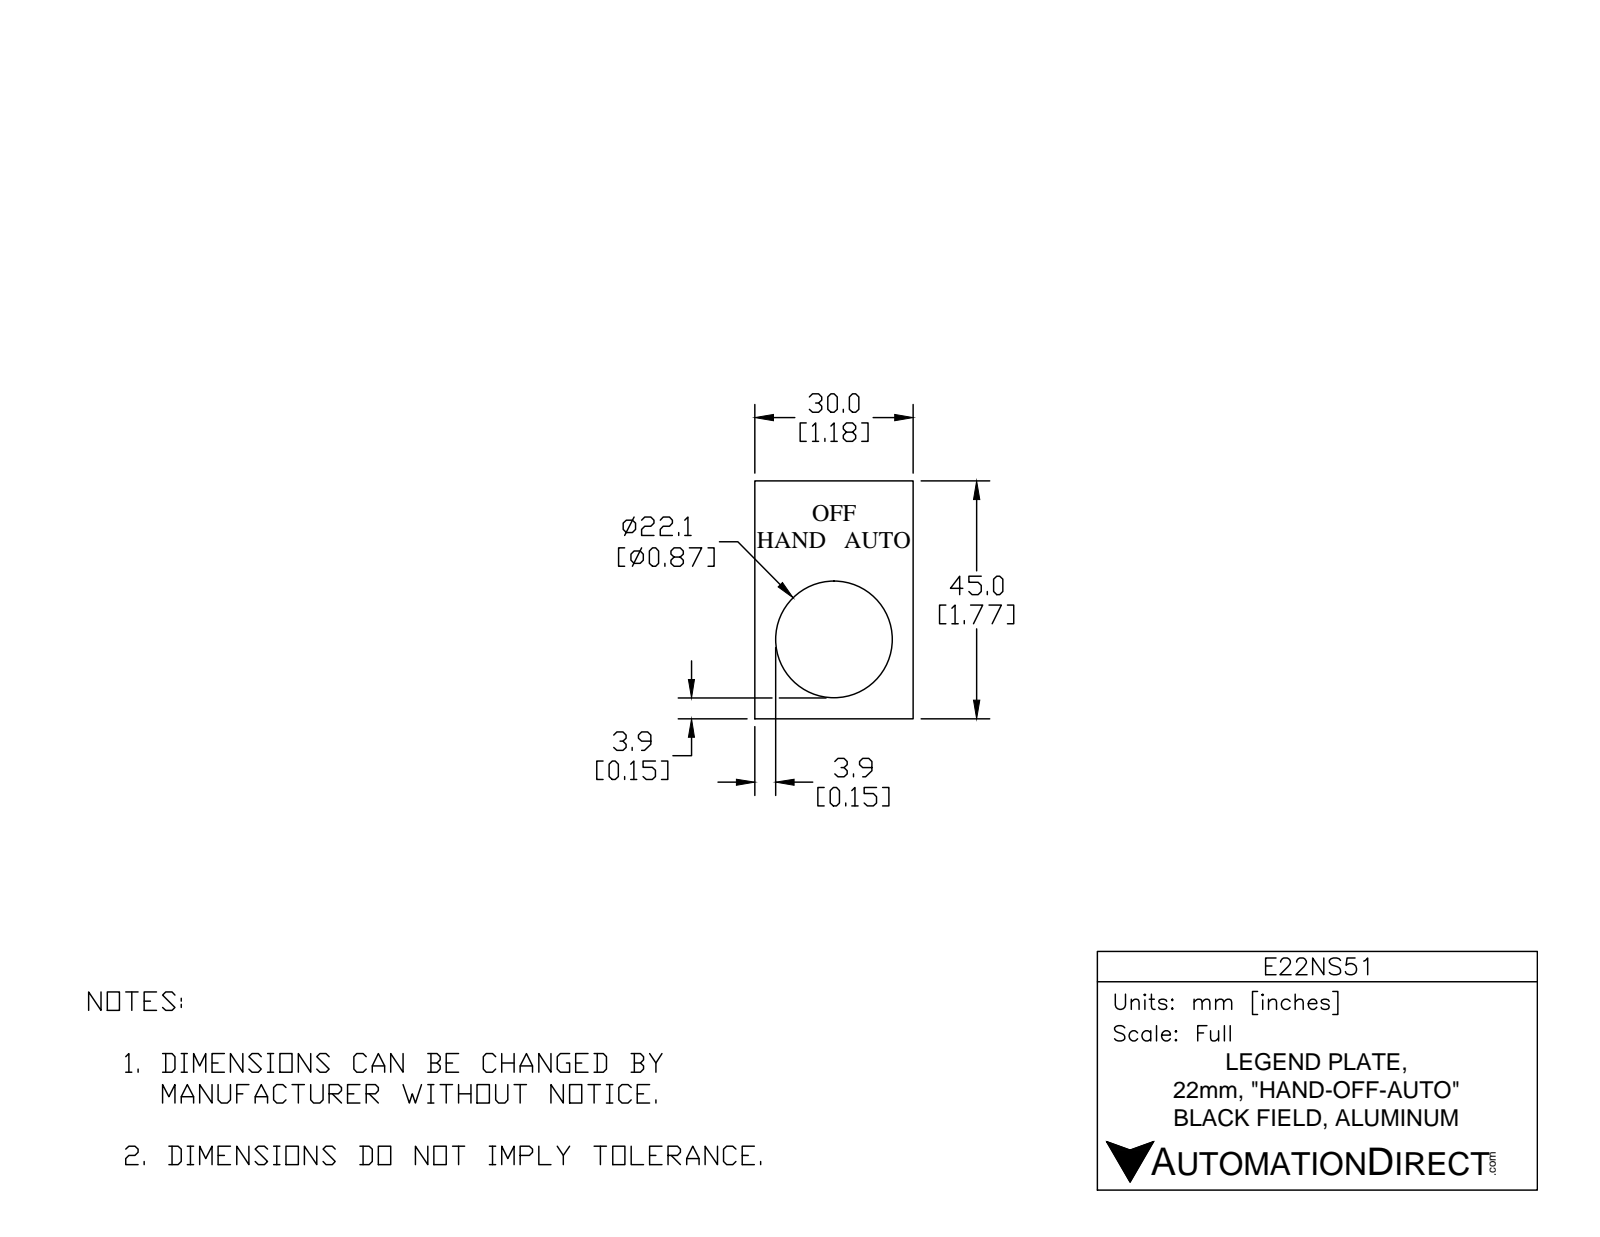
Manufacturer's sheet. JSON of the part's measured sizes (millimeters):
{"part_name": "E22NS51", "step_written_by": "SolidWorks 2017 (AUTOMOTIVE_DESIGN)", "units": "millimeters", "bodies": {"solids": 1, "faces": 149, "planar": 119, "cylindrical": 3, "other": 27}, "overall_size": [45, 30, 1.3], "volume_mm3": 1250, "surface_area_mm2": 2255, "round_holes": [[22.2, 1]], "face_to_face_distances": [1.3, 30, 45, 1.05, 4.7, 40.3, 13.4, 16.6, 6.79, 19.35]}
